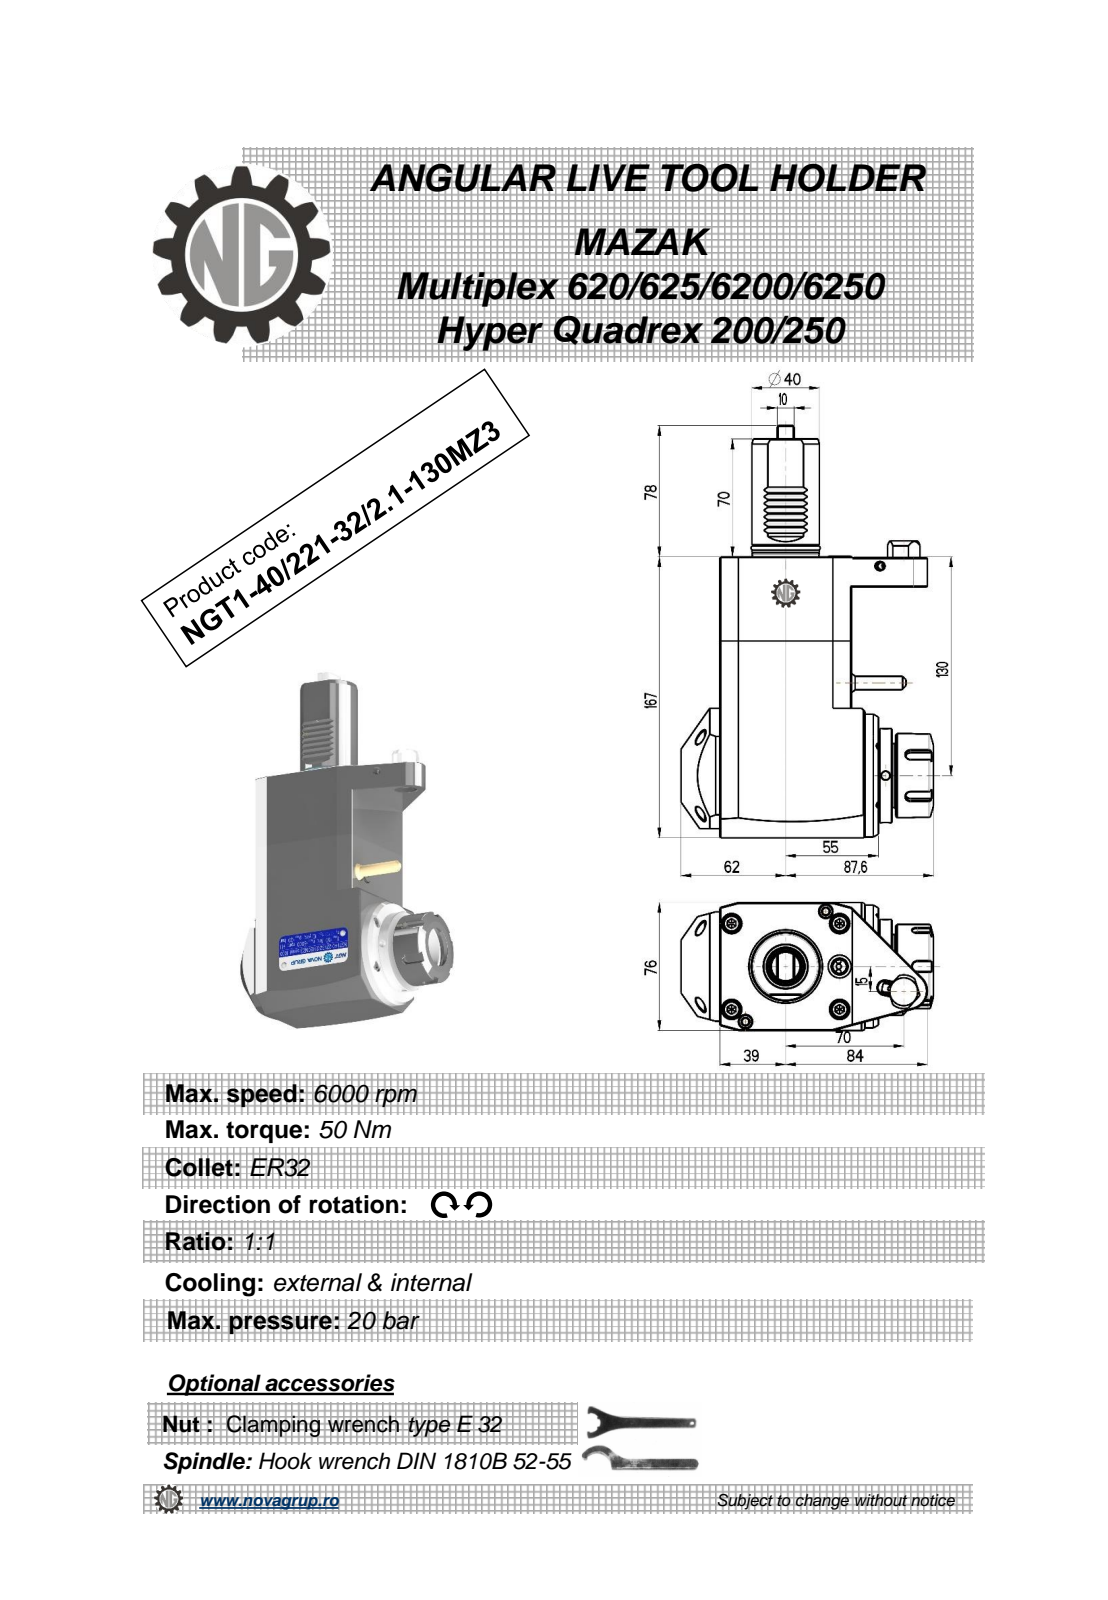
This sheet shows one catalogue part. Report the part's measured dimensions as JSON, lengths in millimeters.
{"part_name": "NGT1_40_221_32_2_1_130MZ3", "step_written_by": "PRO/ENGINEER BY PARAMETRIC TECHNOLOGY CORPORATION, 2010280 (CONFIG_CONTROL_DESIGN)", "units": "millimeters", "bodies": {"solids": 1, "faces": 284, "planar": 135, "cylindrical": 68, "other": 81}, "overall_size": [245, 149.6, 76], "volume_mm3": 1304000, "surface_area_mm2": 90670, "round_holes": [[3, 1], [5, 1], [8, 1], [27, 1]], "round_bosses_or_shafts": [[73, 1], [56, 1], [50, 1], [43, 1], [40, 1], [39.4, 1], [36.2, 1], [10, 1]], "partial_cylinders_radius": [[0.3, 7], [0.2, 6], [3, 5], [0.8, 2], [2.5, 2], [300, 2], [9, 1], [10, 1]], "face_to_face_distances": [76, 78, 167, 87.92, 18, 149, 8, 86, 11, 19], "hole_center_spacings": [60.42]}
